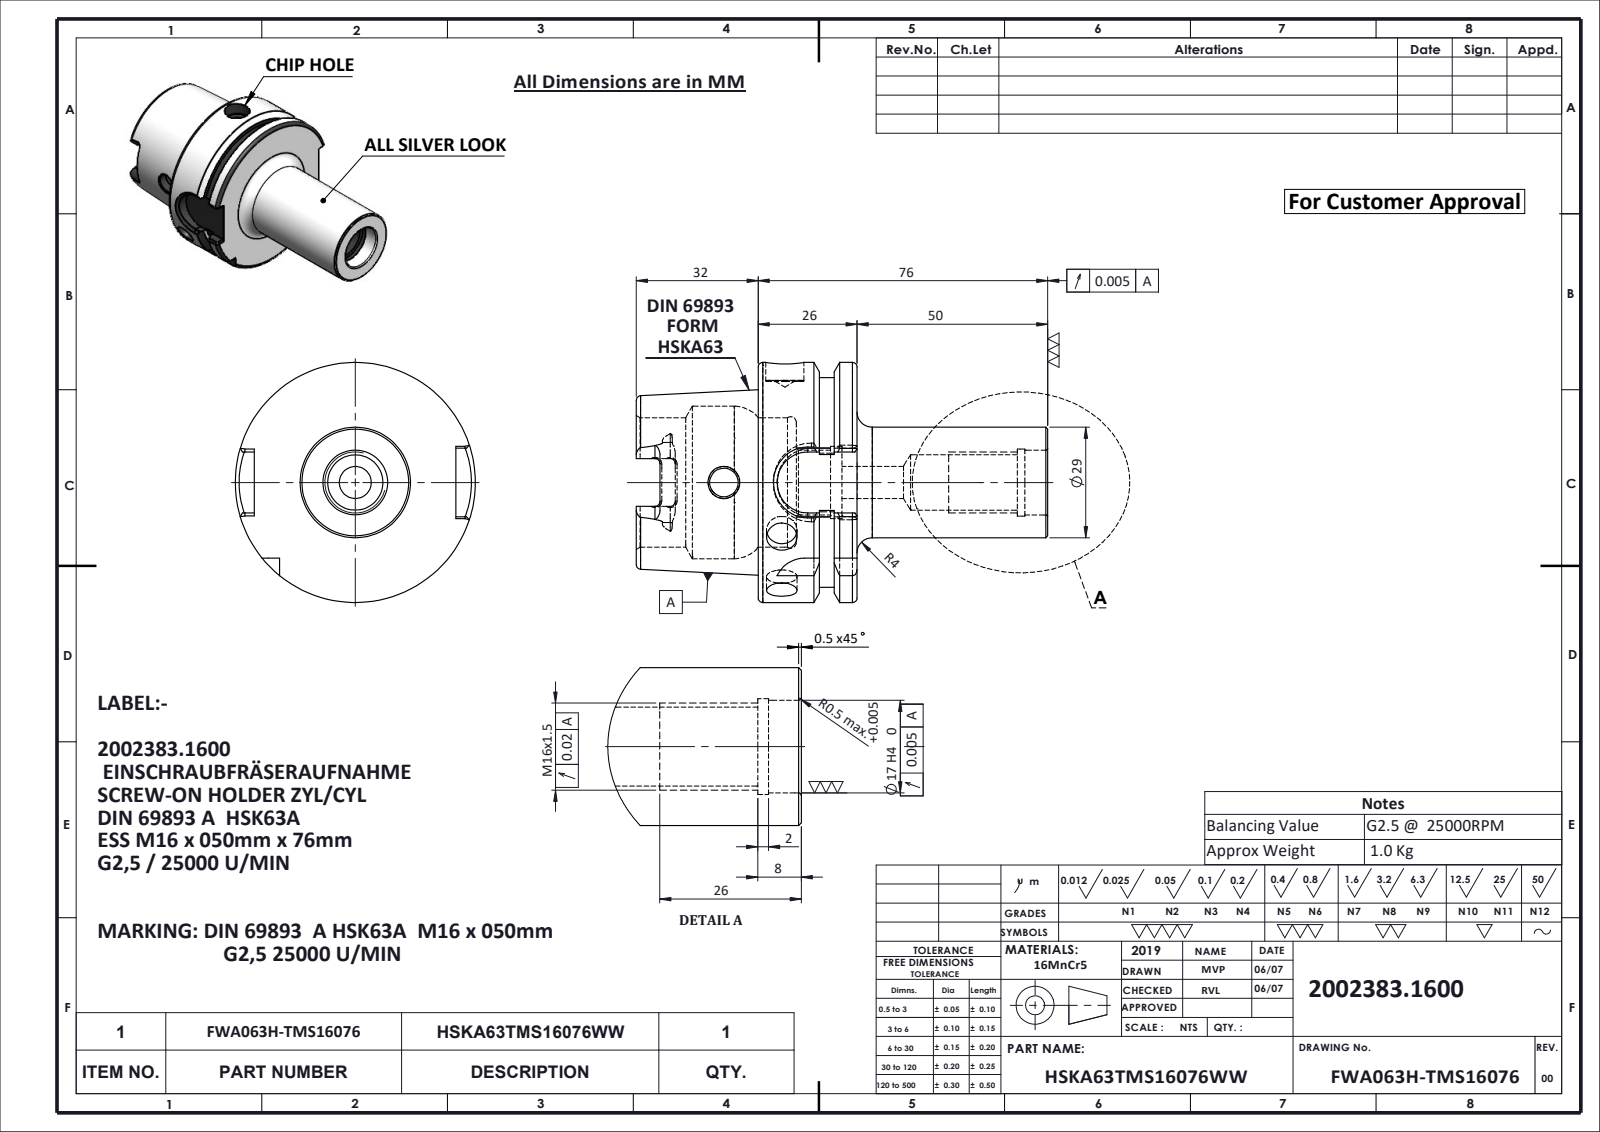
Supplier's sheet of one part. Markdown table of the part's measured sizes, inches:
| quantity | value |
| --- | --- |
| part name | HSKA63TMS16076WW; FWA063H-TMS16076 |
| STEP written by | SolidWorks 2024 (CONFIG_CONTROL_DESIGN) |
| units | inches |
| bodies | 1 solid, 168 faces (51 planar, 53 cylindrical, 64 other) |
| overall size | 4.252 × 2.48 × 2.48 |
| volume | 6.52 in³ |
| surface area | 44.62 in² |
| round holes (diameter × count) | 0.315 × 2, 0.295 × 1, 0.331 × 1, 0.394 × 1, 0.571 × 1, 0.669 × 1, 0.693 × 1, 0.748 × 1, 1.339 × 1, 1.575 × 1 |
| round bosses / shafts (diameter × count) | 2.48 × 1, 2.165 × 1, 1.142 × 1 |
| partial cylindrical surfaces (radius × count) | 0.051 × 6, 0.113 × 4, 0.315 × 2, 0.354 × 1 |
| main face-to-face distances | 1.022, 0.394, 0.628, 2.126, 1.26, 1.654, 2.281, 4.252, 2.992, 2.598 |
